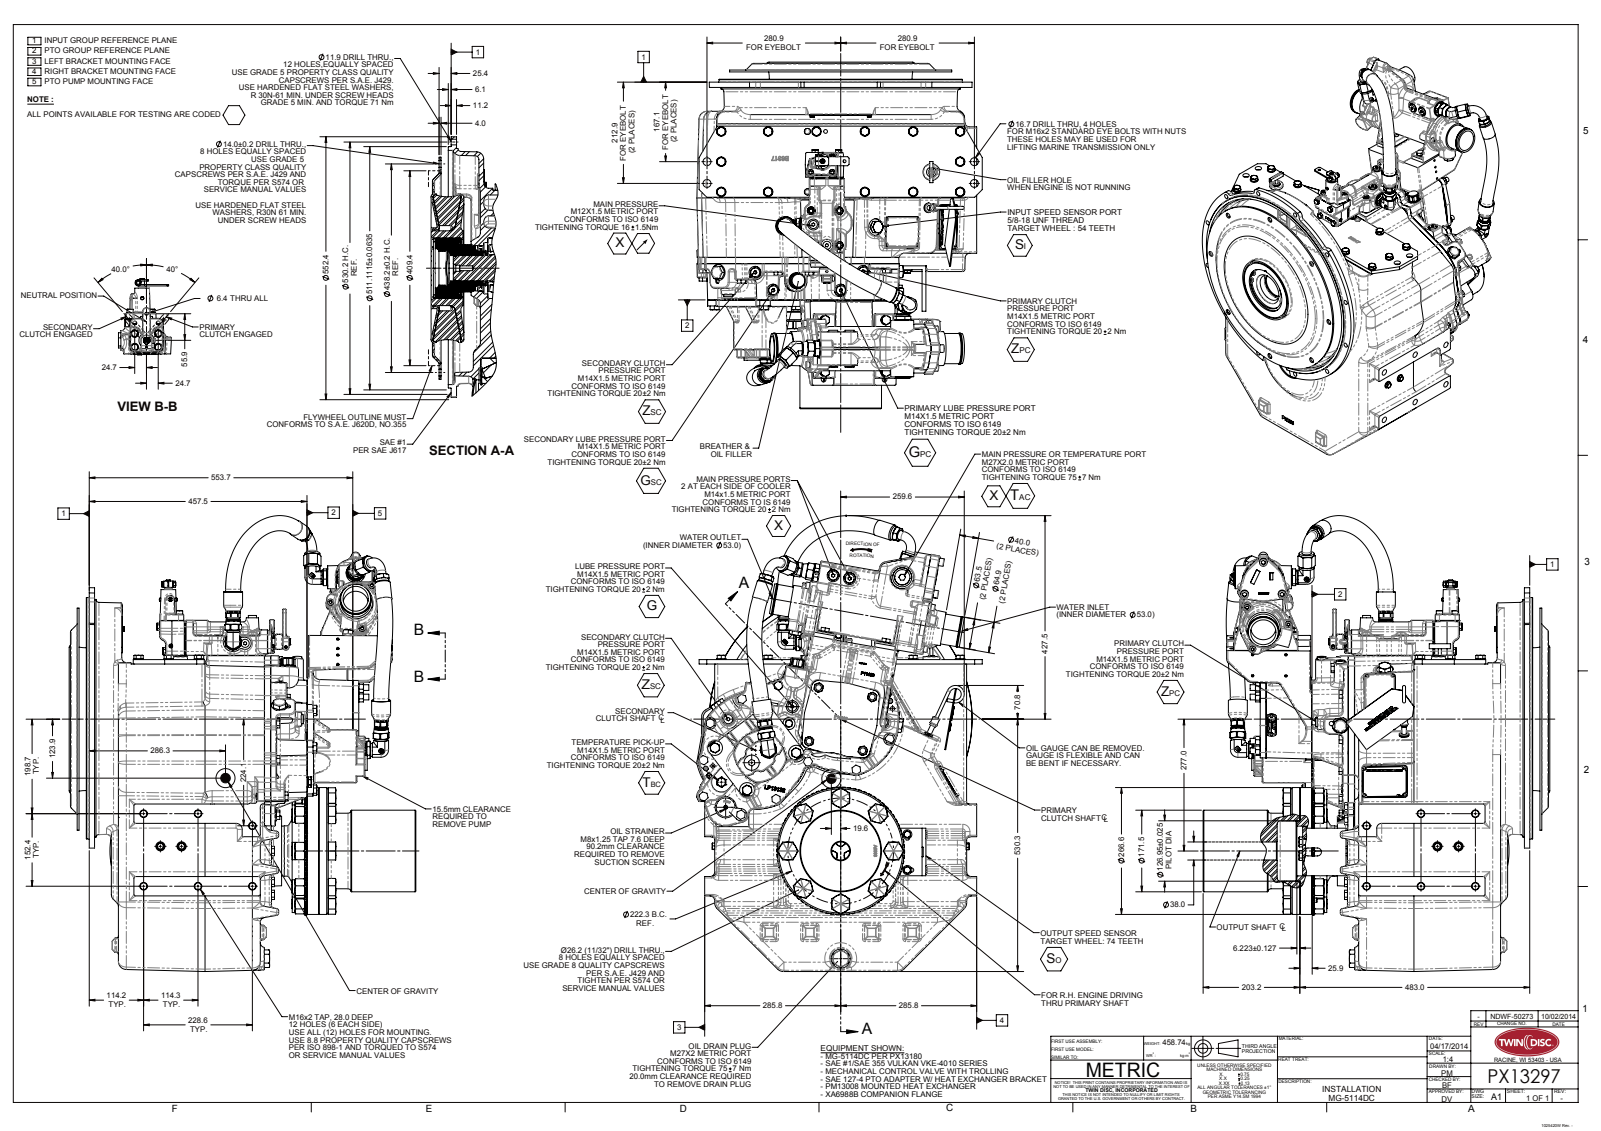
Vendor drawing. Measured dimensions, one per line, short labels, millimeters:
name: PX13297
written by: SolidWorks 2010 (AUTOMOTIVE_DESIGN)
unit: mm
bodies: 0 solids, 6666 faces (2113 planar, 2084 cylindrical, 2469 other)
size: 957.9 × 728.3 × 599.6
holes: 19× ⌀10.7, 12× ⌀11.9, 10× ⌀10.6, 10× ⌀14, 8× ⌀11.2, 6× ⌀5, 6× ⌀16, 4× ⌀6.4, 4× ⌀8, 4× ⌀10.5, 4× ⌀11, 4× ⌀16.5
bosses: 18× ⌀10, 16× ⌀19.8, 10× ⌀19, 10× ⌀13, 8× ⌀36.4, 6× ⌀19.1, 5× ⌀31.8, 5× ⌀16
rounds: 91× R2, 83× R1, 79× R1.5, 72× R5, 66× R45.9, 65× R10, 64× R4, 40× R8
face distances: 320.2, 0.4, 319.8, 9.3, 22, 21.6, 298.2, 4, 478.5, 8.5
hole spacings: 265.1, 137.2, 265.1, 374.9, 459.2, 512.1, 111.1, 127
